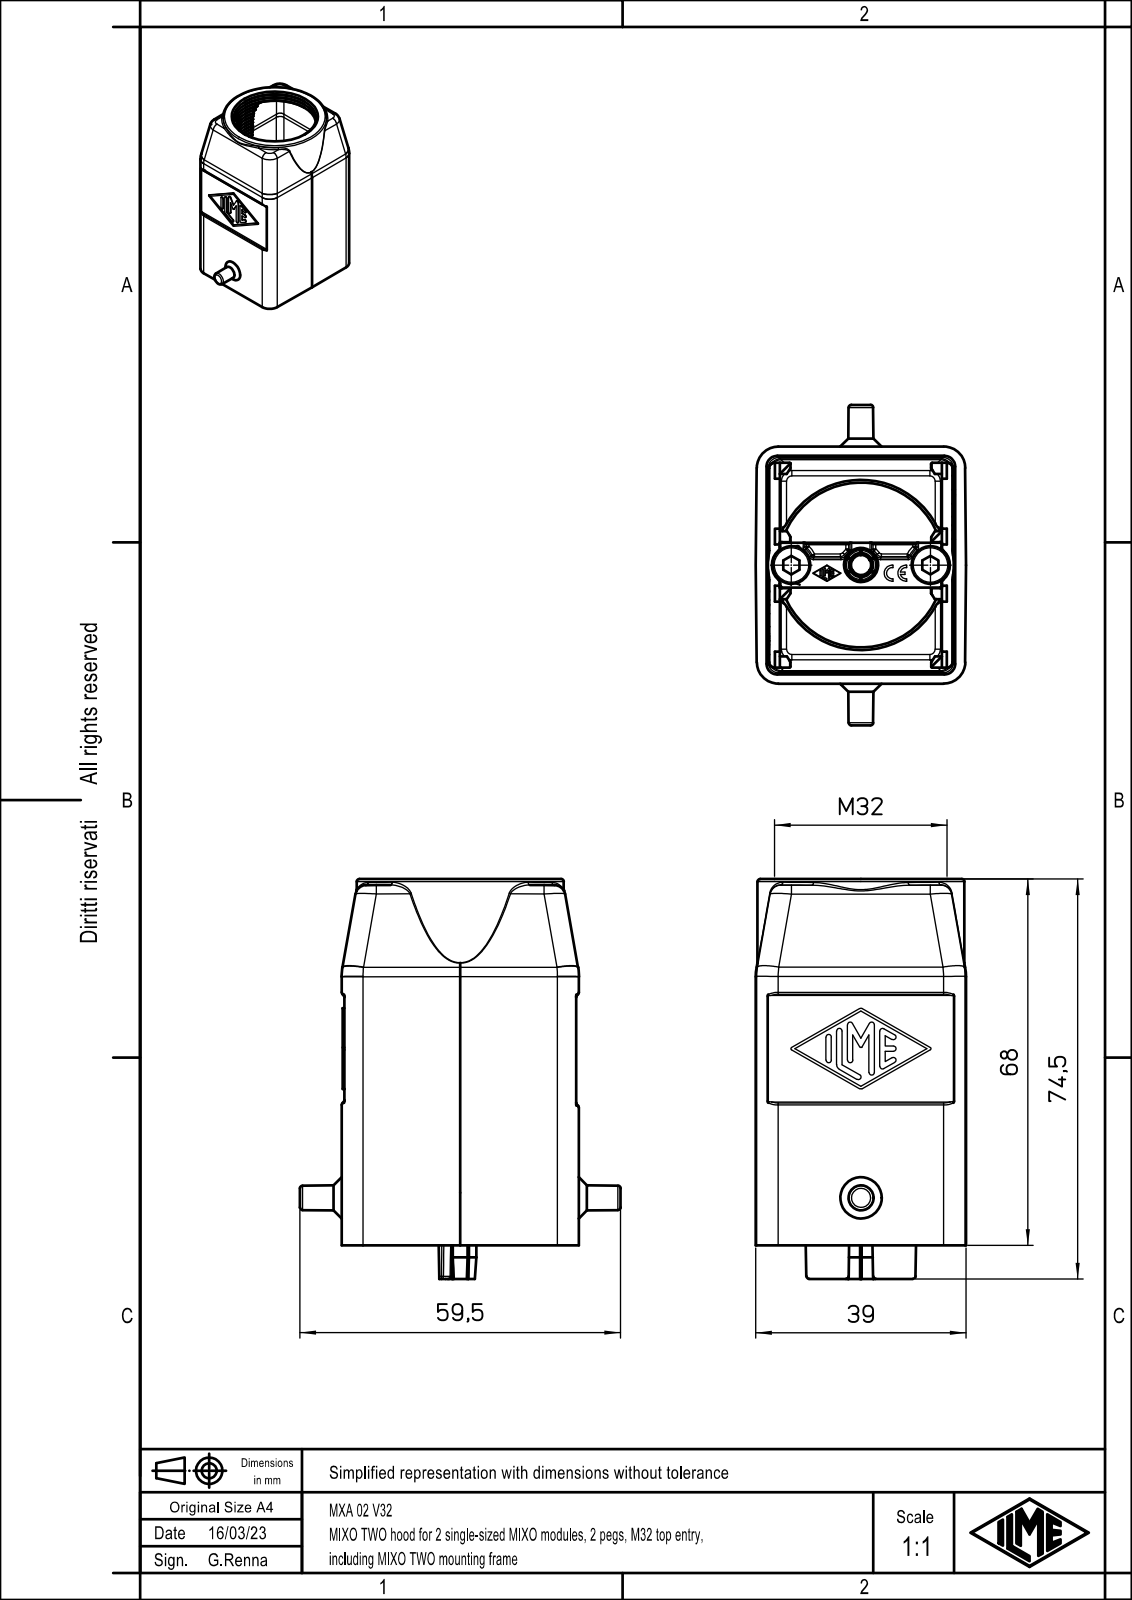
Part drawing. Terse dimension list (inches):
name: MXA 02 V32
written by: Creo Elements/Direct Modeling 20.1B 02-Apr-2019 (C) Parametric Technology GmbH (AUTOMOTIVE_DESIGN)
unit: in
bodies: 1 solid, 1479 faces (628 planar, 309 cylindrical, 542 other)
size: 2.923 × 2.343 × 1.535
volume: 1.863 in³; area: 46.31 in²
holes: 3× ⌀0.165, 1× ⌀0.118
bosses: 2× ⌀0.276, 1× ⌀1.512, 1× ⌀0.236, 1× ⌀0.157, 1× ⌀0.142, 1× ⌀0.107
rounds: 45× R0.004, 38× R0.02, 32× R0.039, 27× R0.012, 15× R0.008, 15× R0.079, 12× R0.059, 12× R0.394
face distances: 1.535, 0.02, 1.713, 1.732, 0.087, 1.693, 0.907, 1.339, 0.079, 0.329
hole spacings: 0.508, 0.213, 0.295, 0.803, 1.016
